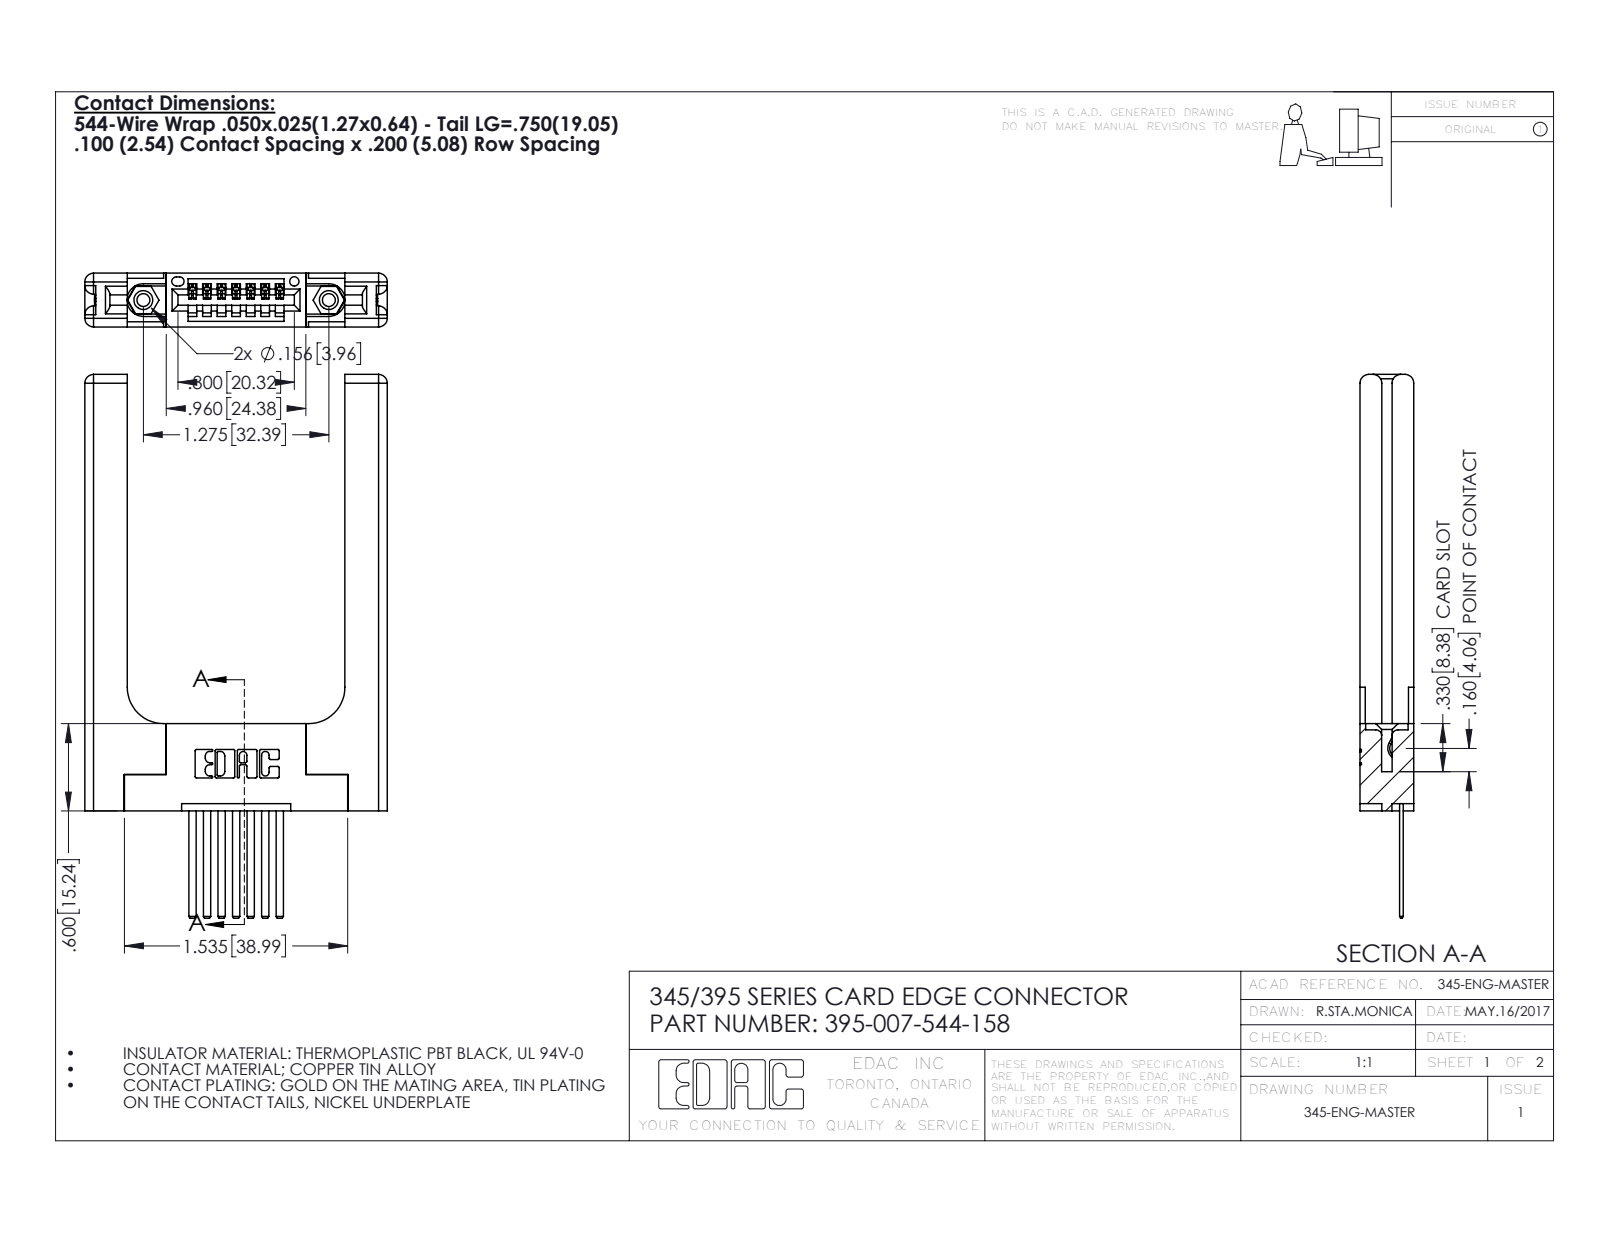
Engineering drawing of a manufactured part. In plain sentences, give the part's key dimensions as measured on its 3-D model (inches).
The part is named "345-250-001_345-250-001-102; 345 Part_Flush Mounting Lugs - 0.156 Dia-TH; 395-007-544-158; 345-220-058_345-220-058 (+1 more)". Its 3-D file was written by "SolidWorks 2016 (CONFIG_CONTROL_DESIGN)". It is 12 solids with 746 faces: 480 planar, 206 cylindrical and 60 other. Overall it measures 3.737 by 2.079 by 0.37 inches. Its volume is 0.813 cubic inches and its surface area 17.77 square inches. Round holes: 2 of diameter 0.089, 2 of diameter 0.125, 2 of diameter 0.156, 1 of diameter 0.064. Round bosses or shafts: 2 of diameter 0.155. Partial cylindrical surfaces (rounded edges, fillets, slot ends): 22 of radius 0.01, 16 of radius 0.06, 14 of radius 0.006, 6 of radius 0.007, 6 of radius 0.031, 3 of radius 0.026, 2 of radius 0.03, 2 of radius 0.031. The main face-to-face distances are 0.37, 0.15, 0.072, 0.22, 0.298, 0.077, 0.148, 1.496, 0.2, 0.071. The hole center spacings are 0.27, 1.045, 1.275.
